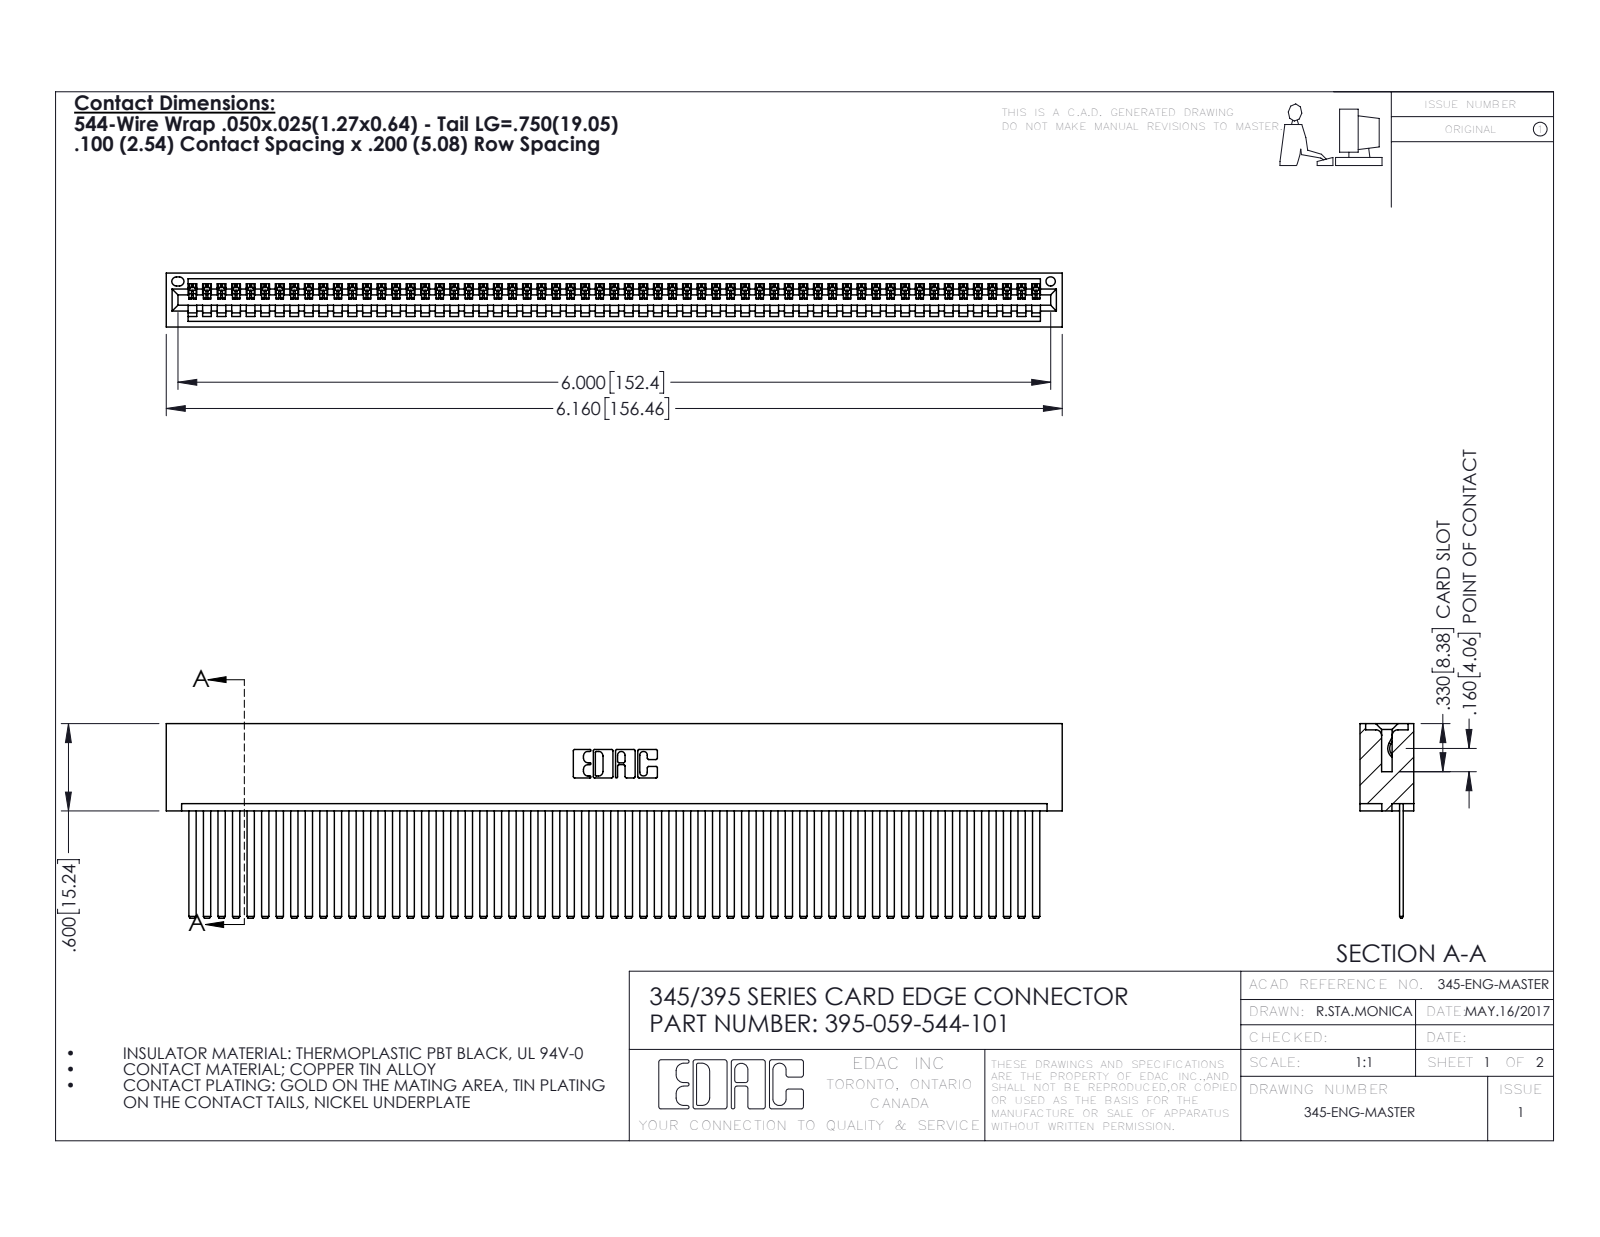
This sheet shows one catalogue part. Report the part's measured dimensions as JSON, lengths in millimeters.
{"part_name": "395-059-544-101; 345-292-001_345-293-144; 345 Part_No Mounting Lugs", "step_written_by": "SolidWorks 2016 (CONFIG_CONTROL_DESIGN)", "units": "millimeters", "bodies": {"solids": 60, "faces": 3186, "planar": 2200, "cylindrical": 986, "other": 0}, "overall_size": [156.5, 34, 9.4], "volume_mm3": 16300, "surface_area_mm2": 24090, "round_holes": [[1.6, 1]], "partial_cylinders_radius": [[0.2, 118], [0.3, 22], [0.2, 6], [0.8, 6], [0.7, 3], [0.8, 2], [1, 2], [0.4, 1]], "face_to_face_distances": [1.8, 7.6, 0.6, 2.5, 6.9, 9.4, 5.1, 5.7, 3.8, 1.8]}
